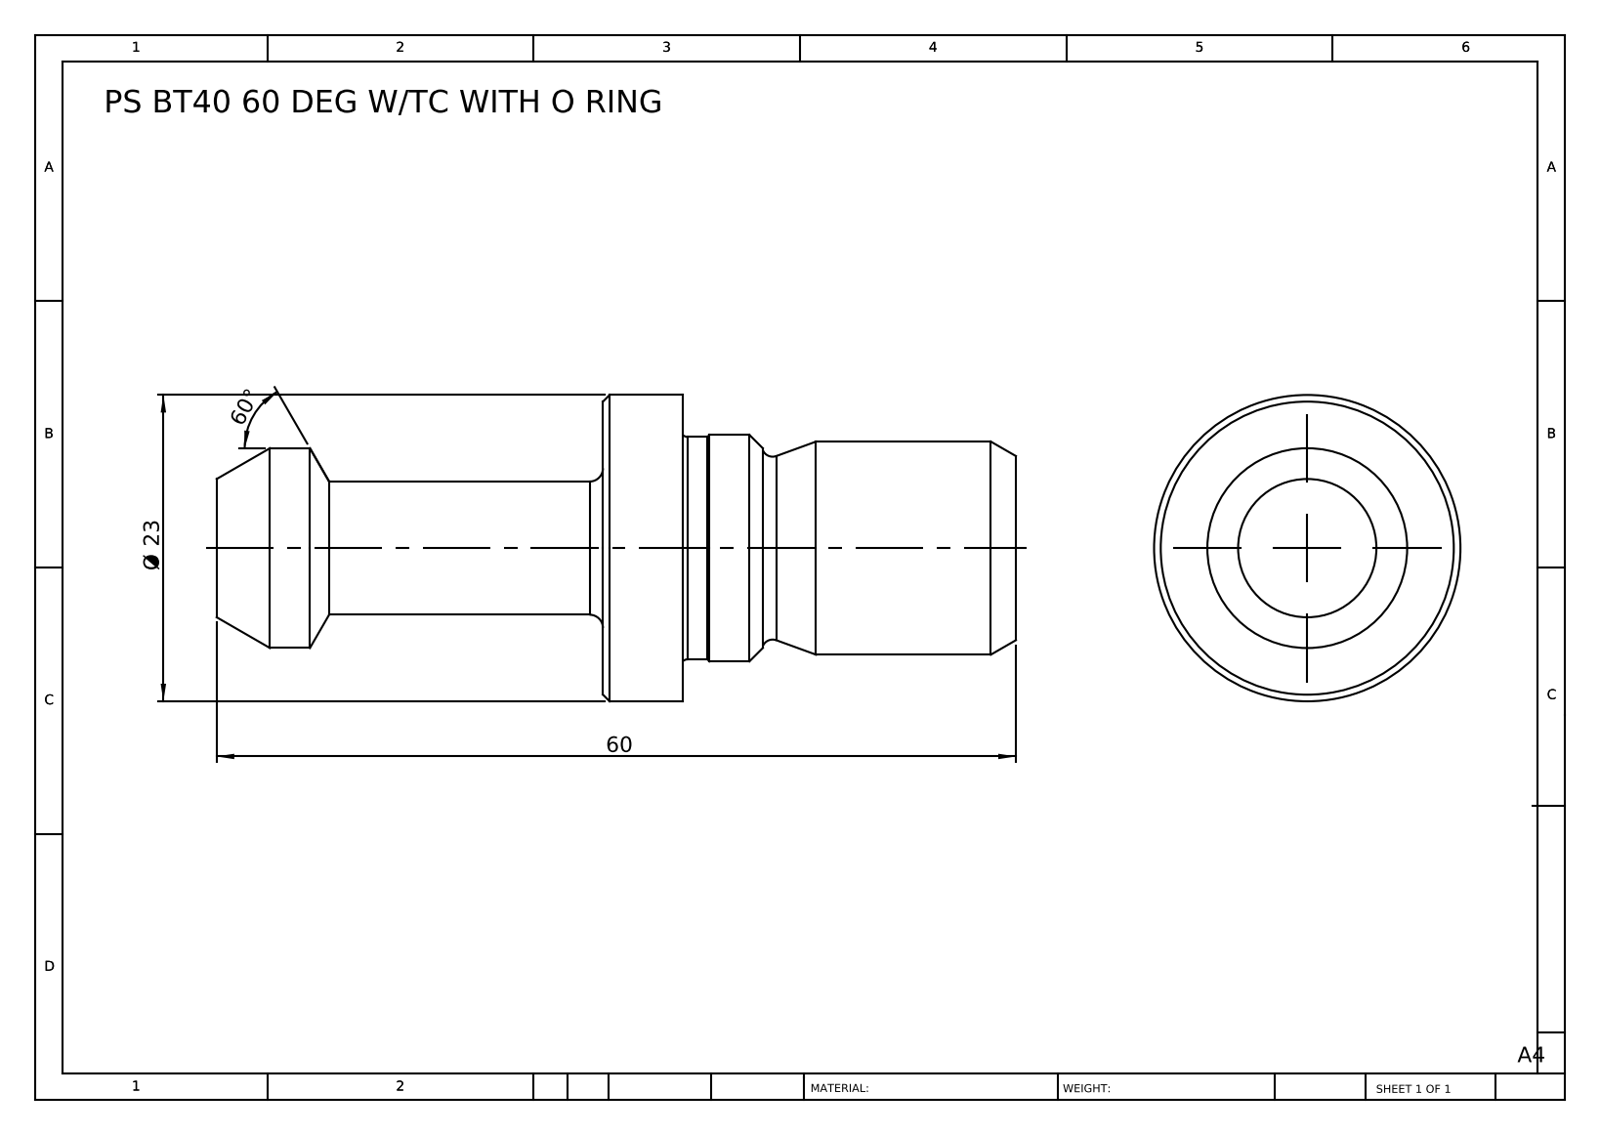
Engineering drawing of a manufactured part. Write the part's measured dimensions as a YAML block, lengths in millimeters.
part_name: "PS BT40 60 DEG W-TC WITH O RING"
step_written_by: "SolidWorks 2014 (CONFIG_CONTROL_DESIGN)"
units: millimeters
bodies: {solids: 1, faces: 41, planar: 5, cylindrical: 12, other: 24}
overall_size: [60, 23, 23]
volume: 10287
surface_area: 3560
round_bosses_or_shafts:
  - {diameter: 23, count: 1}
  - {diameter: 17, count: 1}
  - {diameter: 16.7, count: 1}
  - {diameter: 16, count: 1}
  - {diameter: 15, count: 1}
  - {diameter: 10, count: 1}
face_to_face_distances: [31, 6, 25, 60, 35, 29, 19, 12, 41]
